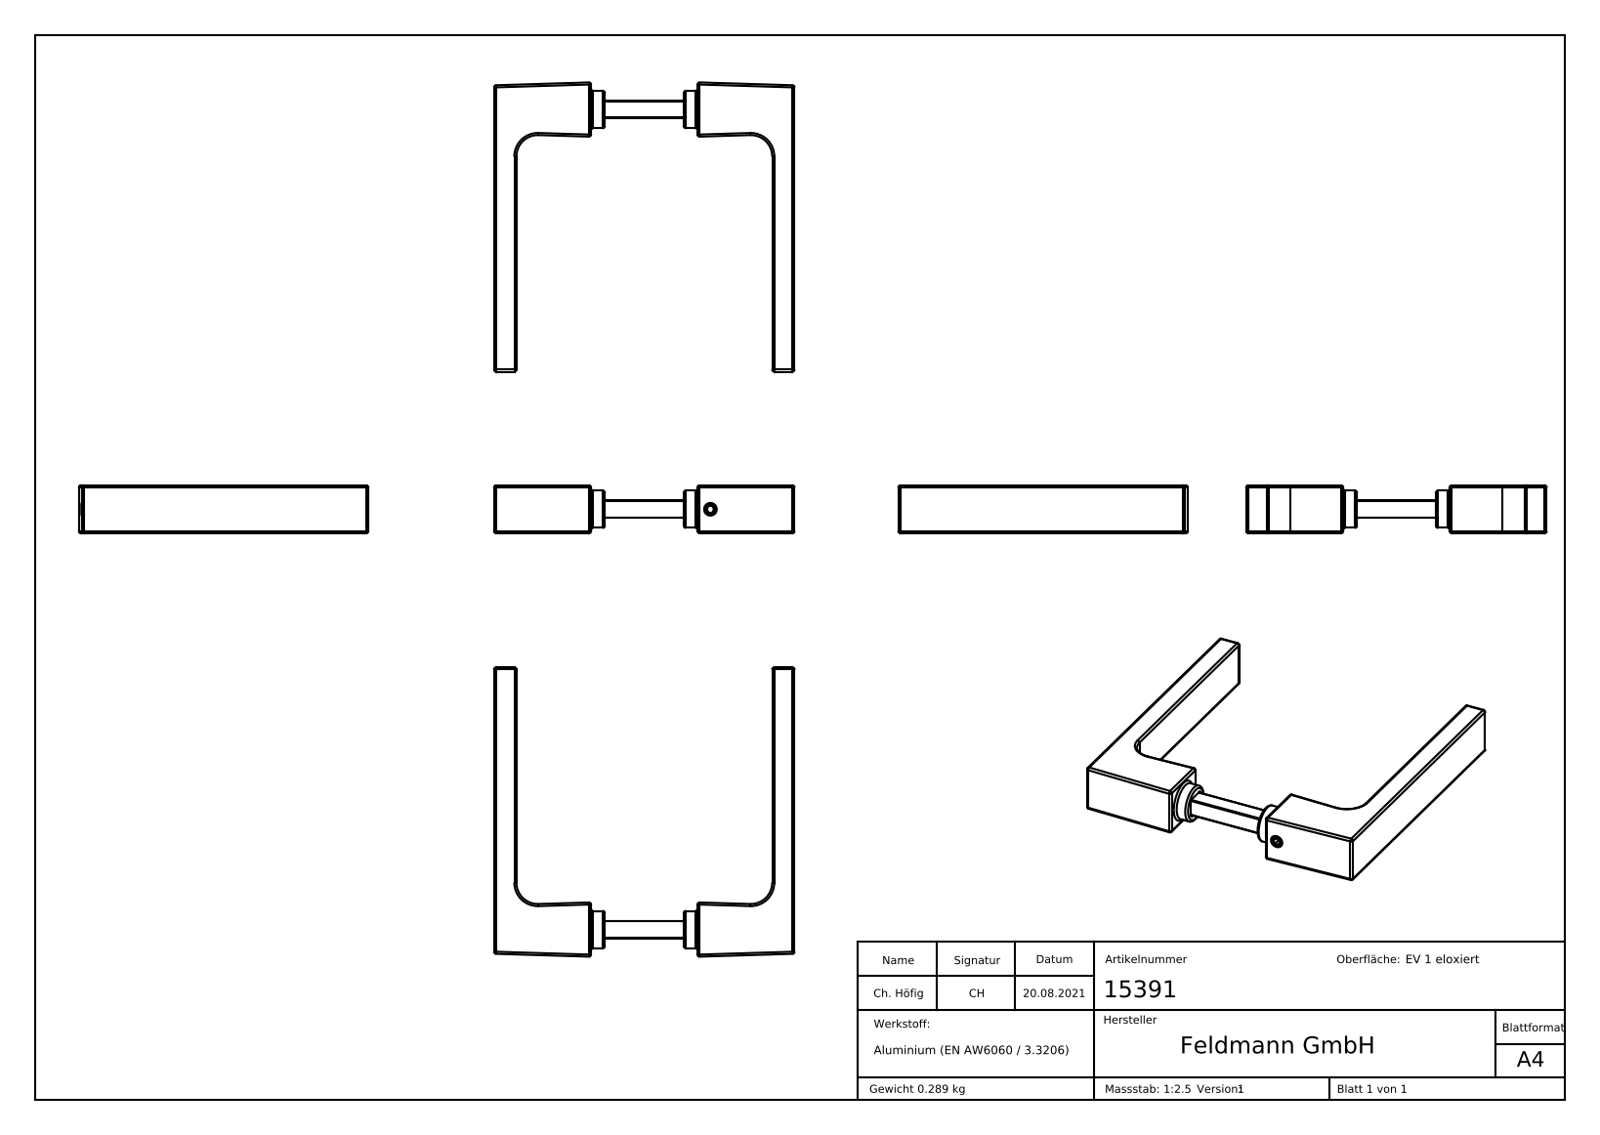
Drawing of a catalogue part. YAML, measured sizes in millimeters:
part_name: "15391; 15391 Teil2; DIN914_DIN 914 M6x8; 15391 Teil1_15391 Teil1 (+3 more)"
step_written_by: "SolidWorks 2018 (CONFIG_CONTROL_DESIGN)"
units: millimeters
bodies: {solids: 4, faces: 326, planar: 150, cylindrical: 52, other: 124}
overall_size: [141, 137.5, 22.5]
volume: 106894
surface_area: 31453
round_holes:
  - {diameter: 5, count: 1}
round_bosses_or_shafts:
  - {diameter: 17.5, count: 1}
  - {diameter: 6, count: 1}
partial_cylinders:
  - {radius: 1, count: 32}
  - {radius: 0.4, count: 4}
  - {radius: 0.5, count: 4}
  - {radius: 10, count: 2}
face_to_face_distances: [10.5, 130.5, 22.5, 141, 120, 8.4, 7.1, 15.4, 8.3, 7]
